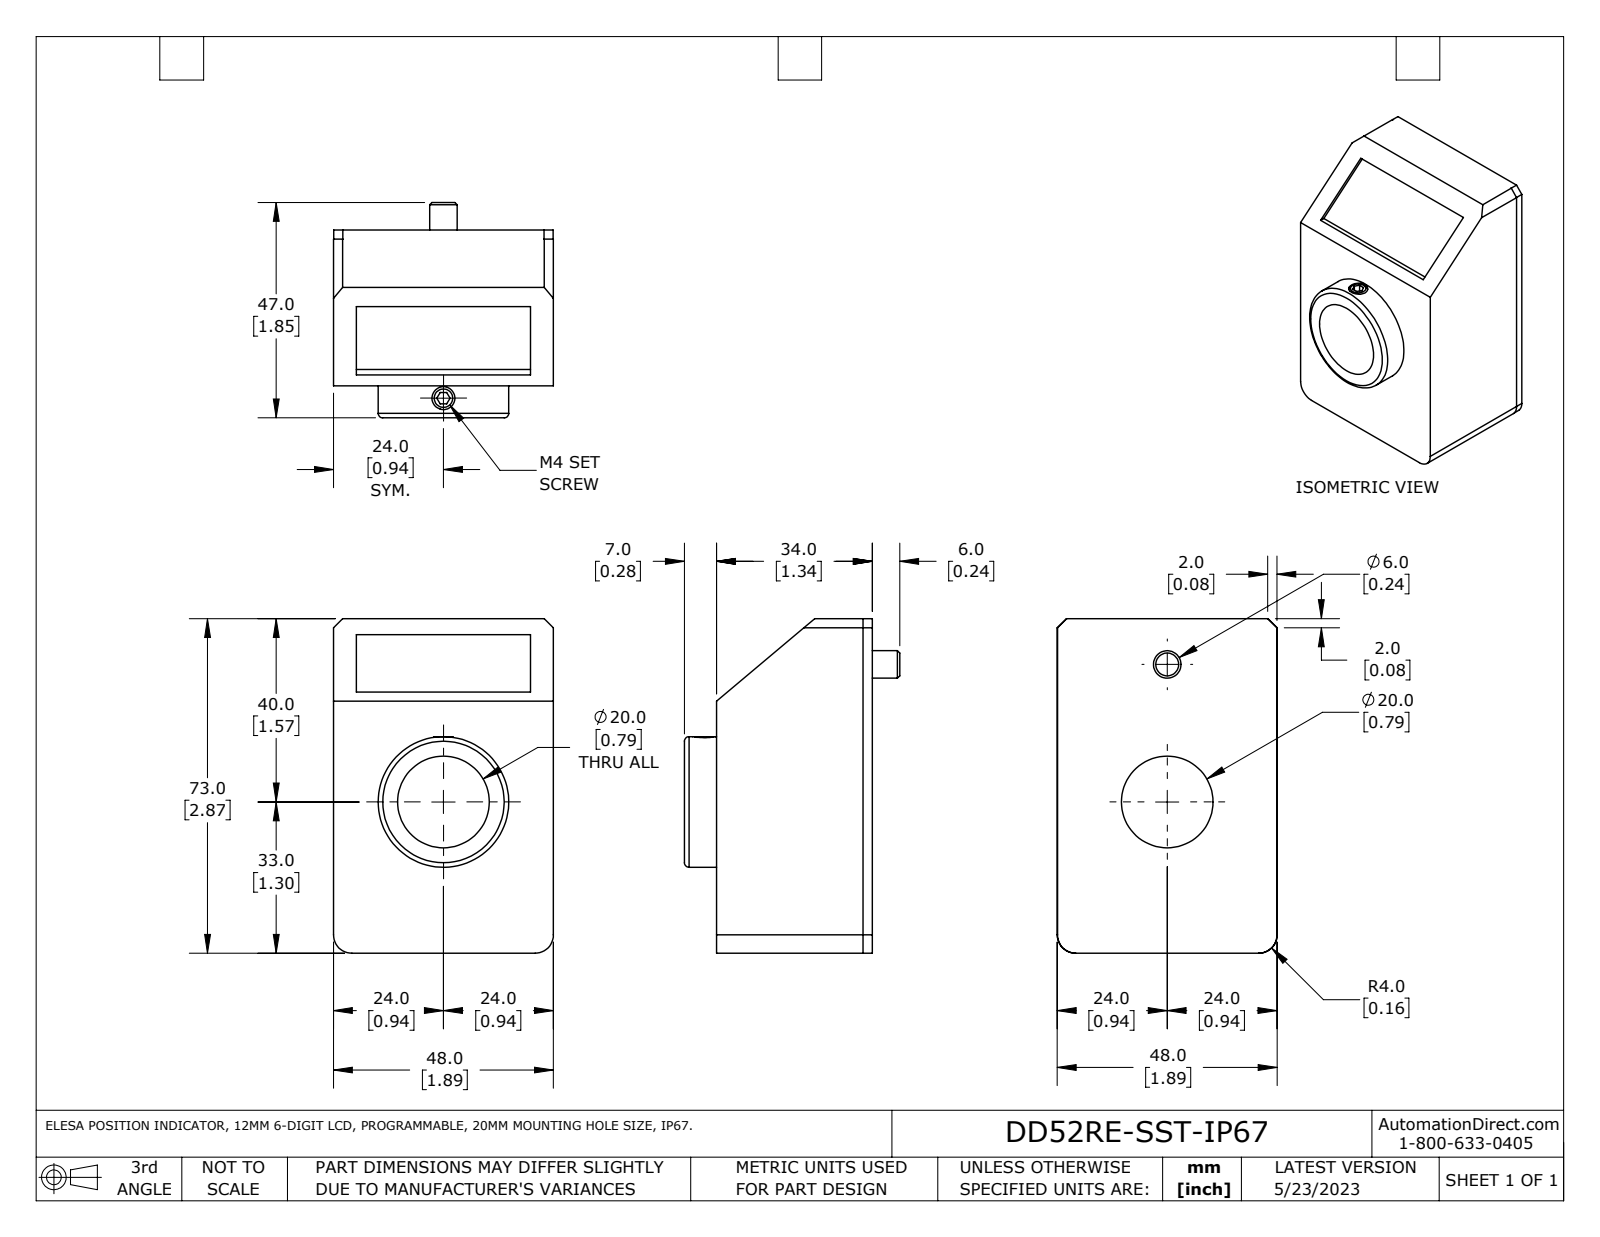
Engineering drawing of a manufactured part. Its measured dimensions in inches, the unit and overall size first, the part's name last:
Units: inches
Overall size (bounding box): 2.874 × 1.89 × 1.85
Round holes (diameter × count): ⌀0.197 ×1, ⌀0.787 ×1, ⌀1.122 ×1
Round bosses / shafts (diameter × count): ⌀0.965 ×1, ⌀0.236 ×1
Partial cylindrical surfaces — rounded edges, fillets, slot ends (radius × count): R0.157 ×4
Main face-to-face distances: 1.339, 1.89, 0.03, 2.874, 1.888, 0.197, 1.142, 0.177, 0.02, 1.161
Volume: 6.076 in³ · Surface area: 26.77 in²
Bodies: 1 solid, 53 faces (38 planar, 11 cylindrical, 4 other)
Part name (STEP PRODUCT): DD52RE-SST-IP67
STEP written by: SolidWorks 2021 (AUTOMOTIVE_DESIGN)
